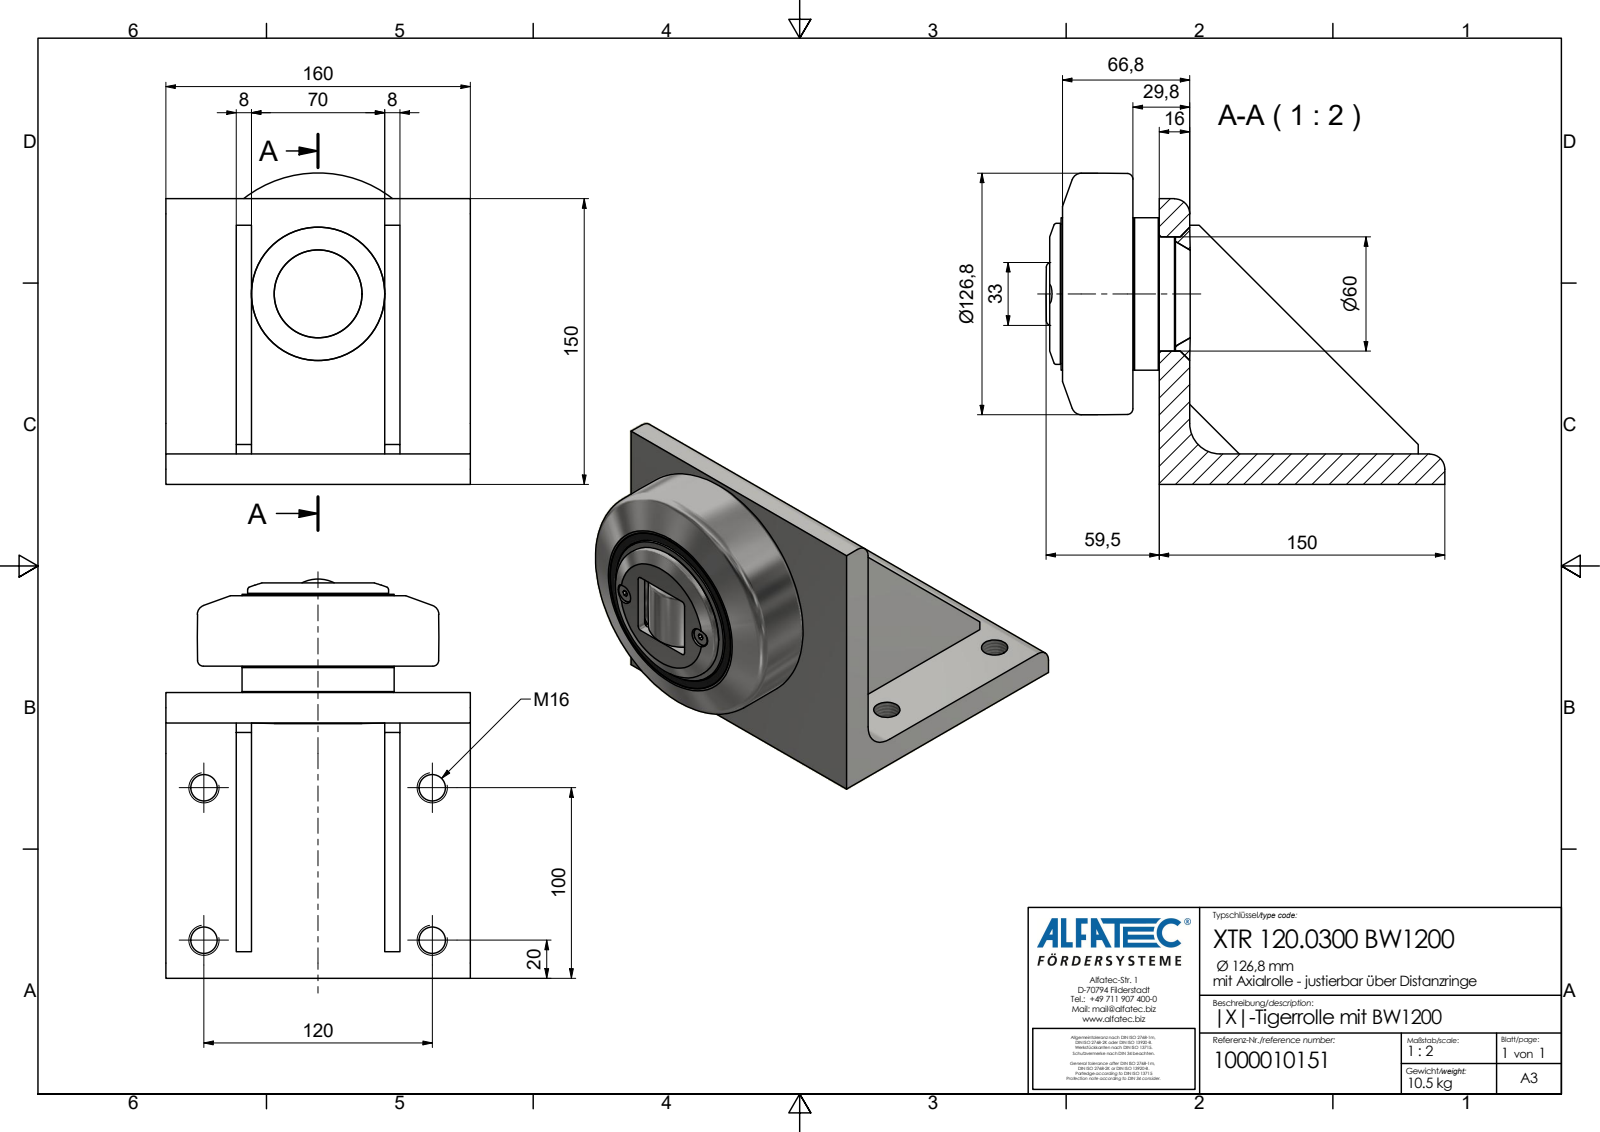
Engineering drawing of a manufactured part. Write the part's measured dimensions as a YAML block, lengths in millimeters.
part_name: "XTR 120.0300 BW1200_Kontur"
step_written_by: "Autodesk Inventor 2020 (AP242_MANAGED_MODEL_BASED_3D_ENGINEERING_MIM_LF)"
units: millimeters
bodies: {solids: 1, faces: 101, planar: 55, cylindrical: 27, other: 19}
overall_size: [209.5, 163.4, 160]
volume: 1382000
surface_area: 168258
round_holes:
  - {diameter: 13.84, count: 4}
  - {diameter: 10.5, count: 2}
round_bosses_or_shafts:
  - {diameter: 9.75, count: 2}
  - {diameter: 80, count: 1}
  - {diameter: 74, count: 1}
partial_cylinders:
  - {radius: 2, count: 4}
  - {radius: 8, count: 2}
  - {radius: 11.5, count: 1}
  - {radius: 14, count: 1}
  - {radius: 16, count: 1}
  - {radius: 24, count: 1}
face_to_face_distances: [16, 8, 78, 37, 45, 115, 123, 86, 70, 29.8]
hole_center_spacings: [80, 120, 144.22, 56]
